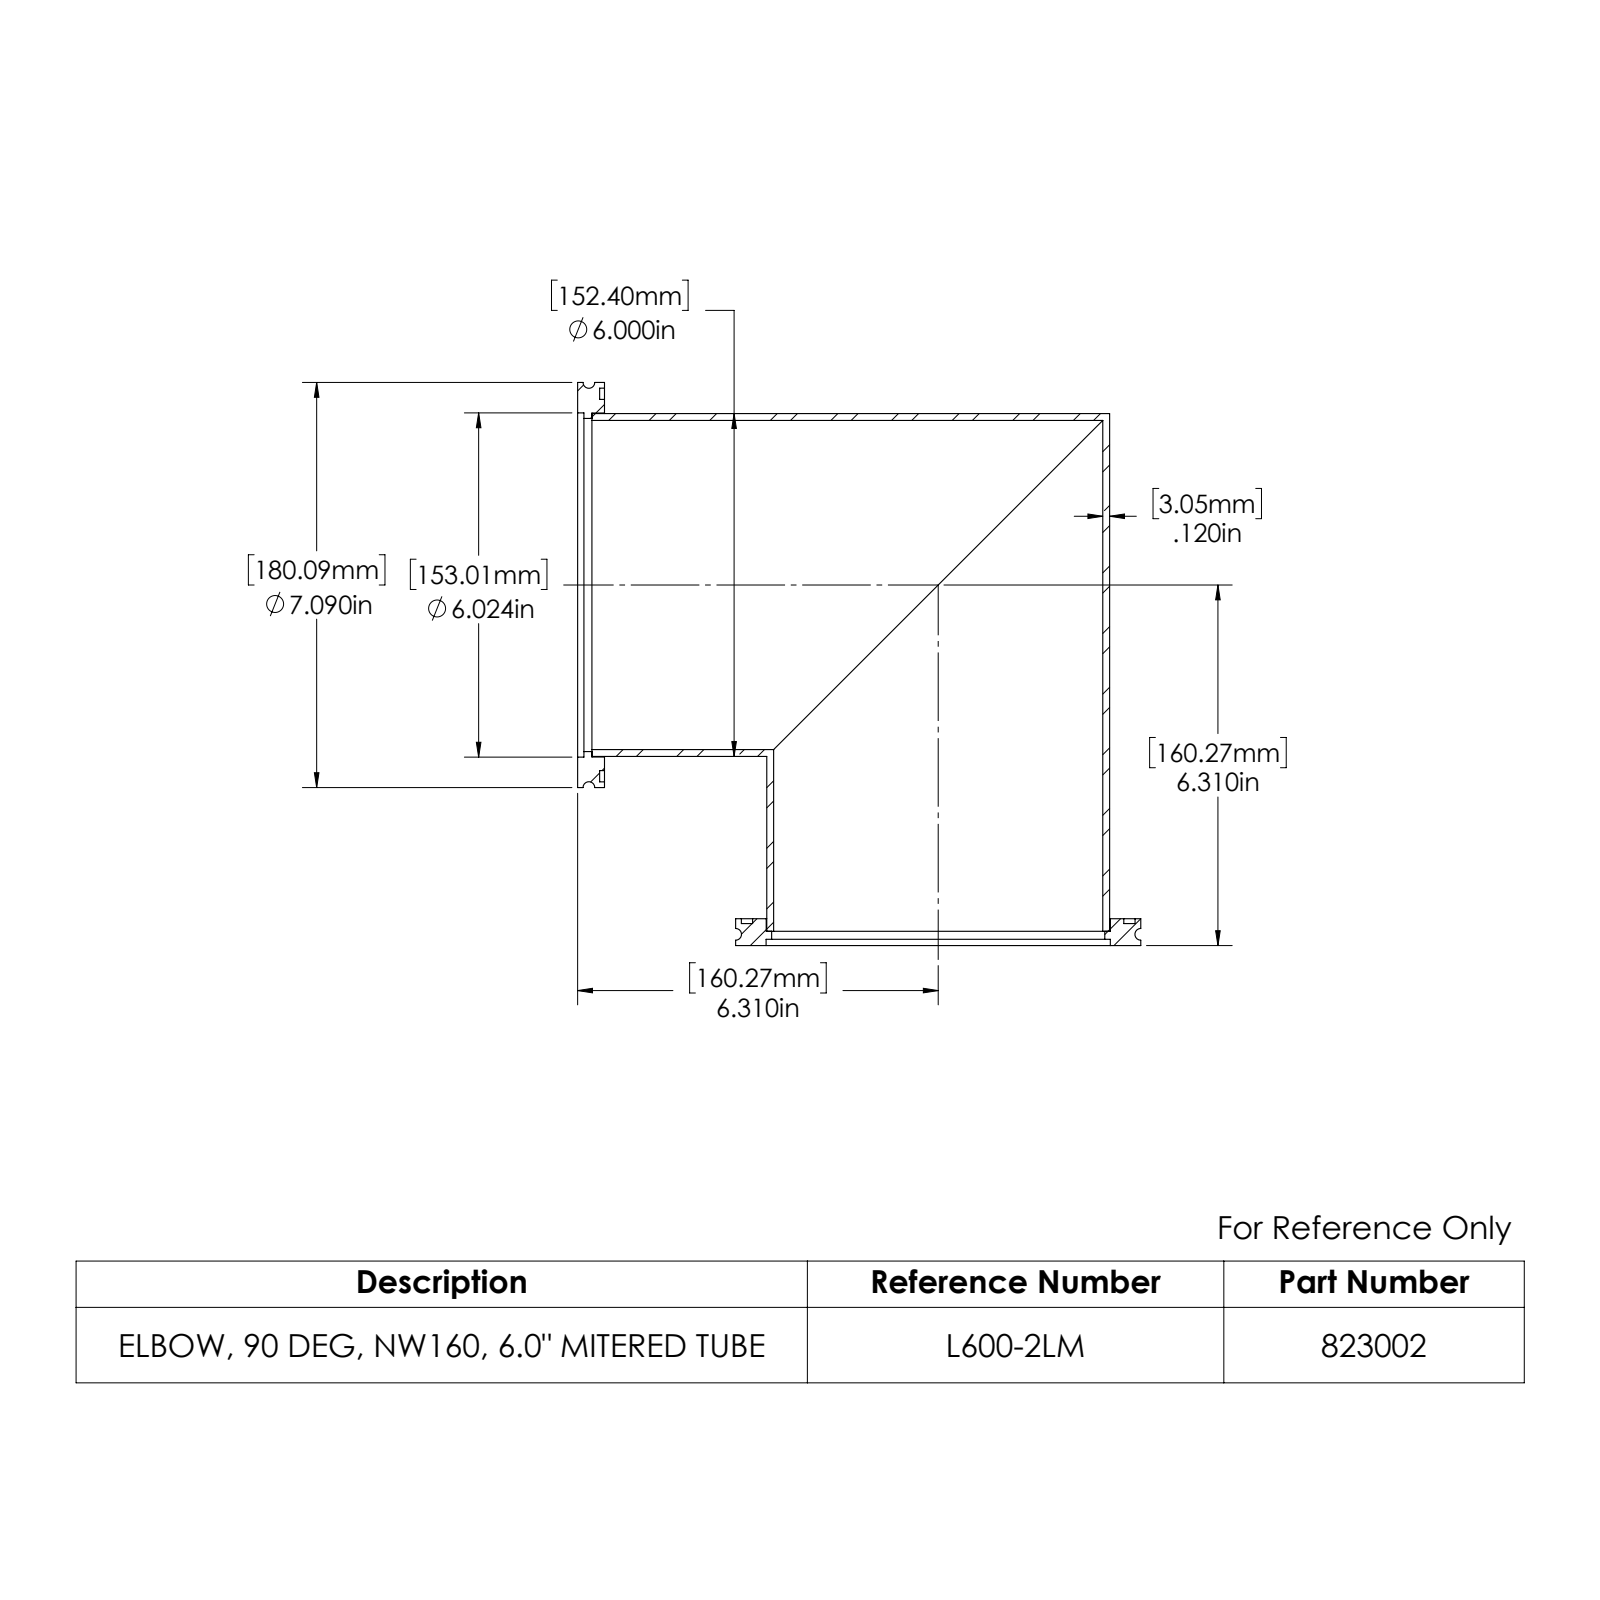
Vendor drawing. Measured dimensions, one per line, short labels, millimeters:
name: 823002; 813002; 940308
written by: SolidWorks 2022 (AUTOMOTIVE_DESIGN)
unit: mm
bodies: 3 solids, 58 faces (14 planar, 36 cylindrical, 8 other)
size: 273.5 × 253.1 × 250.3
volume: 594 400 mm³; area: 357 400 mm²
holes: 2× ⌀146.3, 2× ⌀148.1, 2× ⌀152.9, 2× ⌀153, 2× ⌀175
bosses: 2× ⌀180.1, 2× ⌀165, 2× ⌀152.4
face distances: 11.9, 2.2, 9.8, 5.6, 3.4, 6.4, 9.1, 7, 3.6, 2.8
